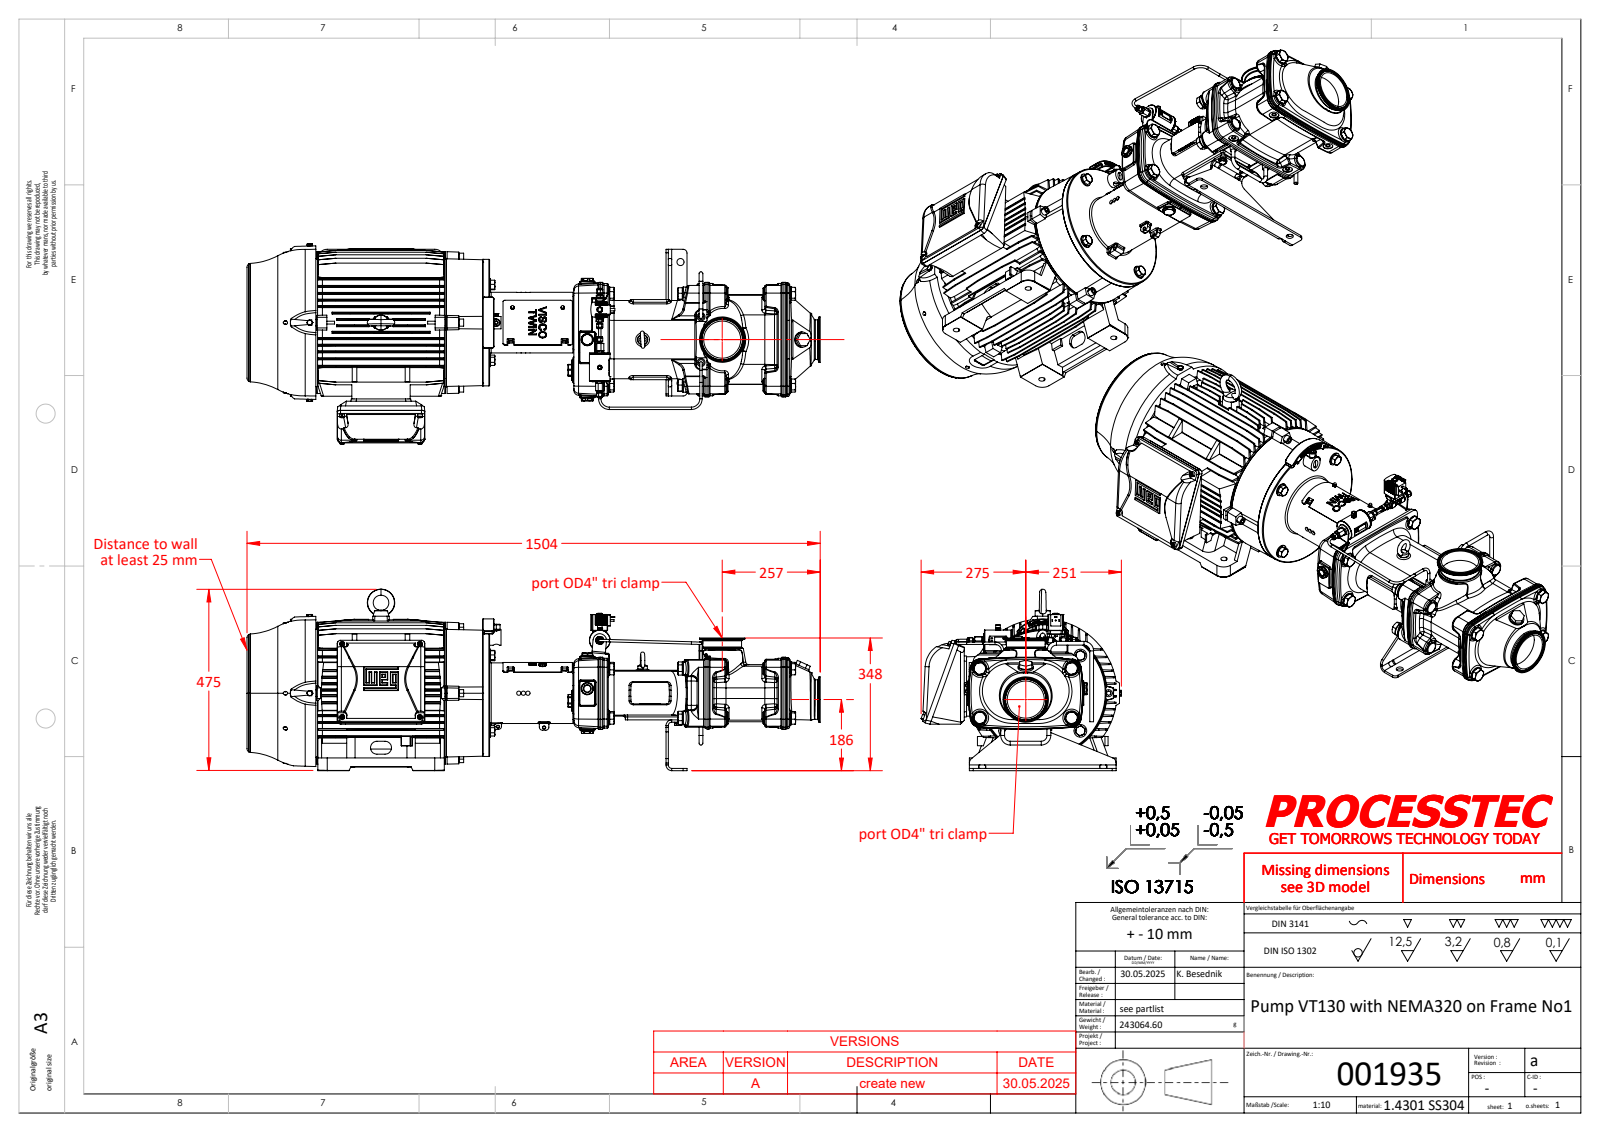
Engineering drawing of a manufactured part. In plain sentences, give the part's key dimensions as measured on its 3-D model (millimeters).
The part is named "001379; 001090_ISO 2338 - 8 h8 x 20 - A1; 001313_DIN 1587 - M5; Teil4^001381 (+8 more)". Its 3-D file was written by "SolidWorks 2023 (AUTOMOTIVE_DESIGN)". It is 92 solids with 8205 faces: 2659 planar, 2444 cylindrical and 3102 other. Overall it measures 1504.41 by 525.98 by 476.2 millimeters. Its volume is 88 460 000 cubic millimeters and its surface area 4 989 000 square millimeters. Round holes: 9 of diameter 8, 9 of diameter 8.5, 9 of diameter 17.5, 6 of diameter 14, 5 of diameter 4.1, 5 of diameter 7.6, 5 of diameter 9, 5 of diameter 17, 5 of diameter 18, 4 of diameter 5, 4 of diameter 15.88, 4 of diameter 16.66. Round bosses or shafts: 10 of diameter 10, 9 of diameter 8, 7 of diameter 11.6, 6 of diameter 20, 5 of diameter 16, 5 of diameter 6.3, 5 of diameter 6, 4 of diameter 33.32. Partial cylindrical surfaces (rounded edges, fillets, slot ends): 188 of radius 2.98, 93 of radius 3, 39 of radius 2, 33 of radius 1.5, 23 of radius 8, 21 of radius 5, 19 of radius 4, 19 of radius 6. The main face-to-face distances are 342.3, 303.5, 481, 747.8, 405.5, 102, 444.3, 1228.8, 886.5, 784.5. The hole center spacings are 55, 129.3, 87.73, 136.25, 162.84, 193.35, 28.75, 64.65.
